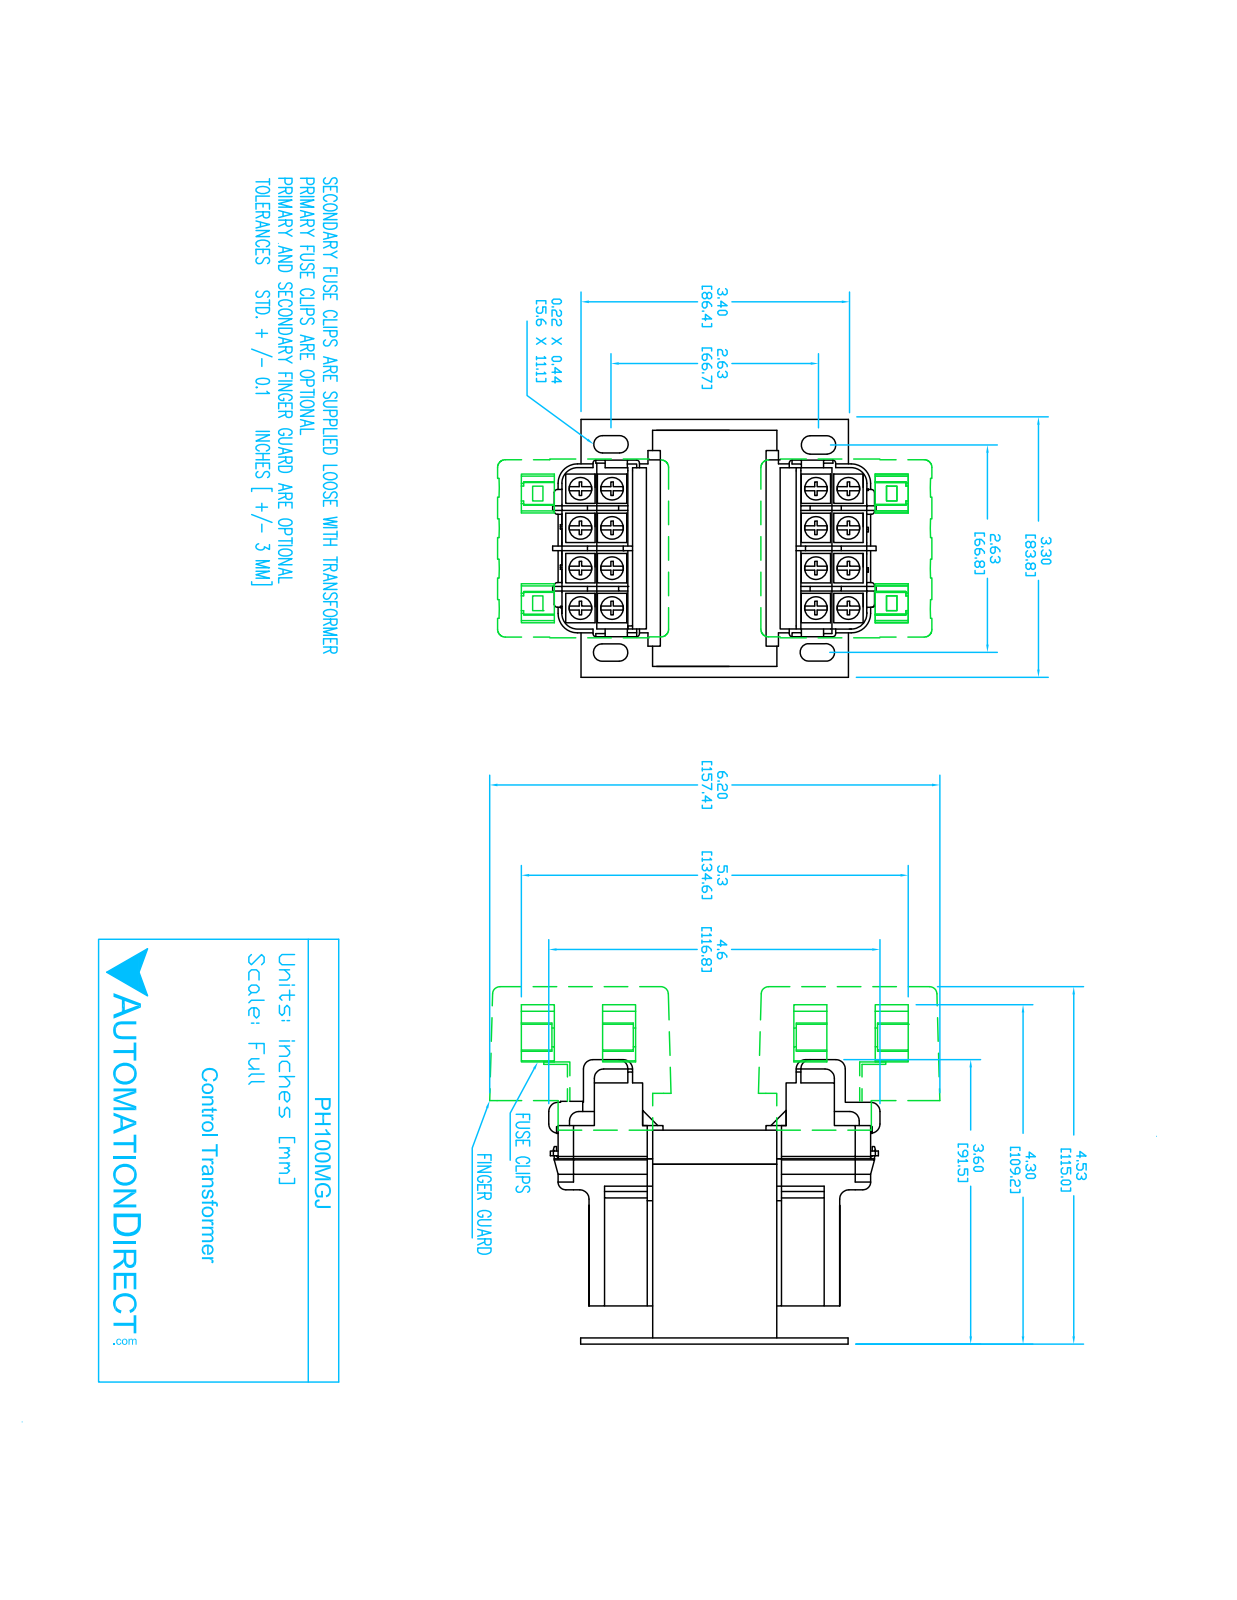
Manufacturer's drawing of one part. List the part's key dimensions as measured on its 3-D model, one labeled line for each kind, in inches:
Part name (STEP PRODUCT): PH100MGJ
STEP written by: SolidWorks 2017 (AUTOMOTIVE_DESIGN)
Units: inches
Bodies: 8 solids, 496 faces (288 planar, 148 cylindrical, 60 other)
Overall size (bounding box): 4.567 × 3.514 × 3.25
Volume: 29.38 in³ · Surface area: 125.8 in²
Round holes (diameter × count): ⌀0.157 ×4
Partial cylindrical surfaces — rounded edges, fillets, slot ends (radius × count): R0.039 ×46, R0.079 ×28, R0.11 ×8, R0.197 ×8, R0.118 ×4, R0.246 ×4
Main face-to-face distances: 2.136, 1.969, 0.136, 0.364, 2, 0.398, 2.602, 2.5, 0.118, 0.5
Hole centre spacings: 1.128, 2.624, 2.857
